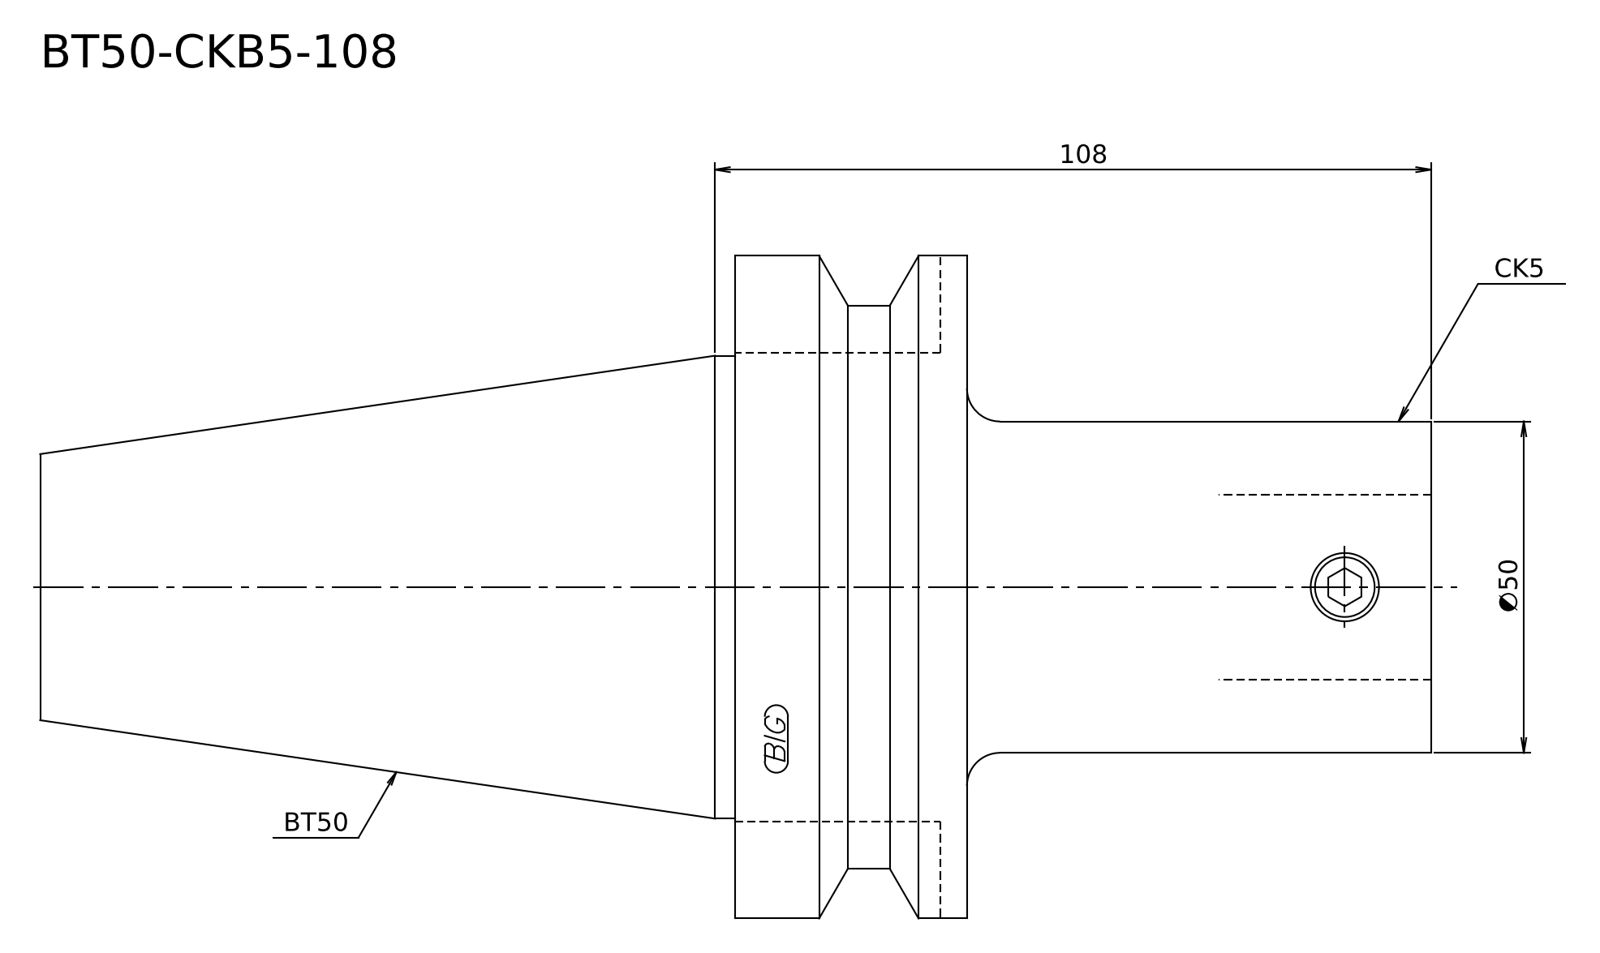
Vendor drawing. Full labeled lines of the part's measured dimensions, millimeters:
STEP written by: Kubotek KeyCreator V8.5.1 (14335) (CONFIG_CONTROL_DESIGN)
Units: millimetres
Bodies: 1 solid, 13 faces (4 planar, 5 cylindrical, 4 other)
Overall size (bounding box): 209.8 × 100 × 100
Volume: 650 184 mm³ · Surface area: 55 156 mm²
Round bosses / shafts (diameter × count): ⌀100 ×1, ⌀85 ×1, ⌀69.85 ×1, ⌀50 ×1
Main face-to-face distances: 35, 70, 105, 209.8, 139.8, 104.8
